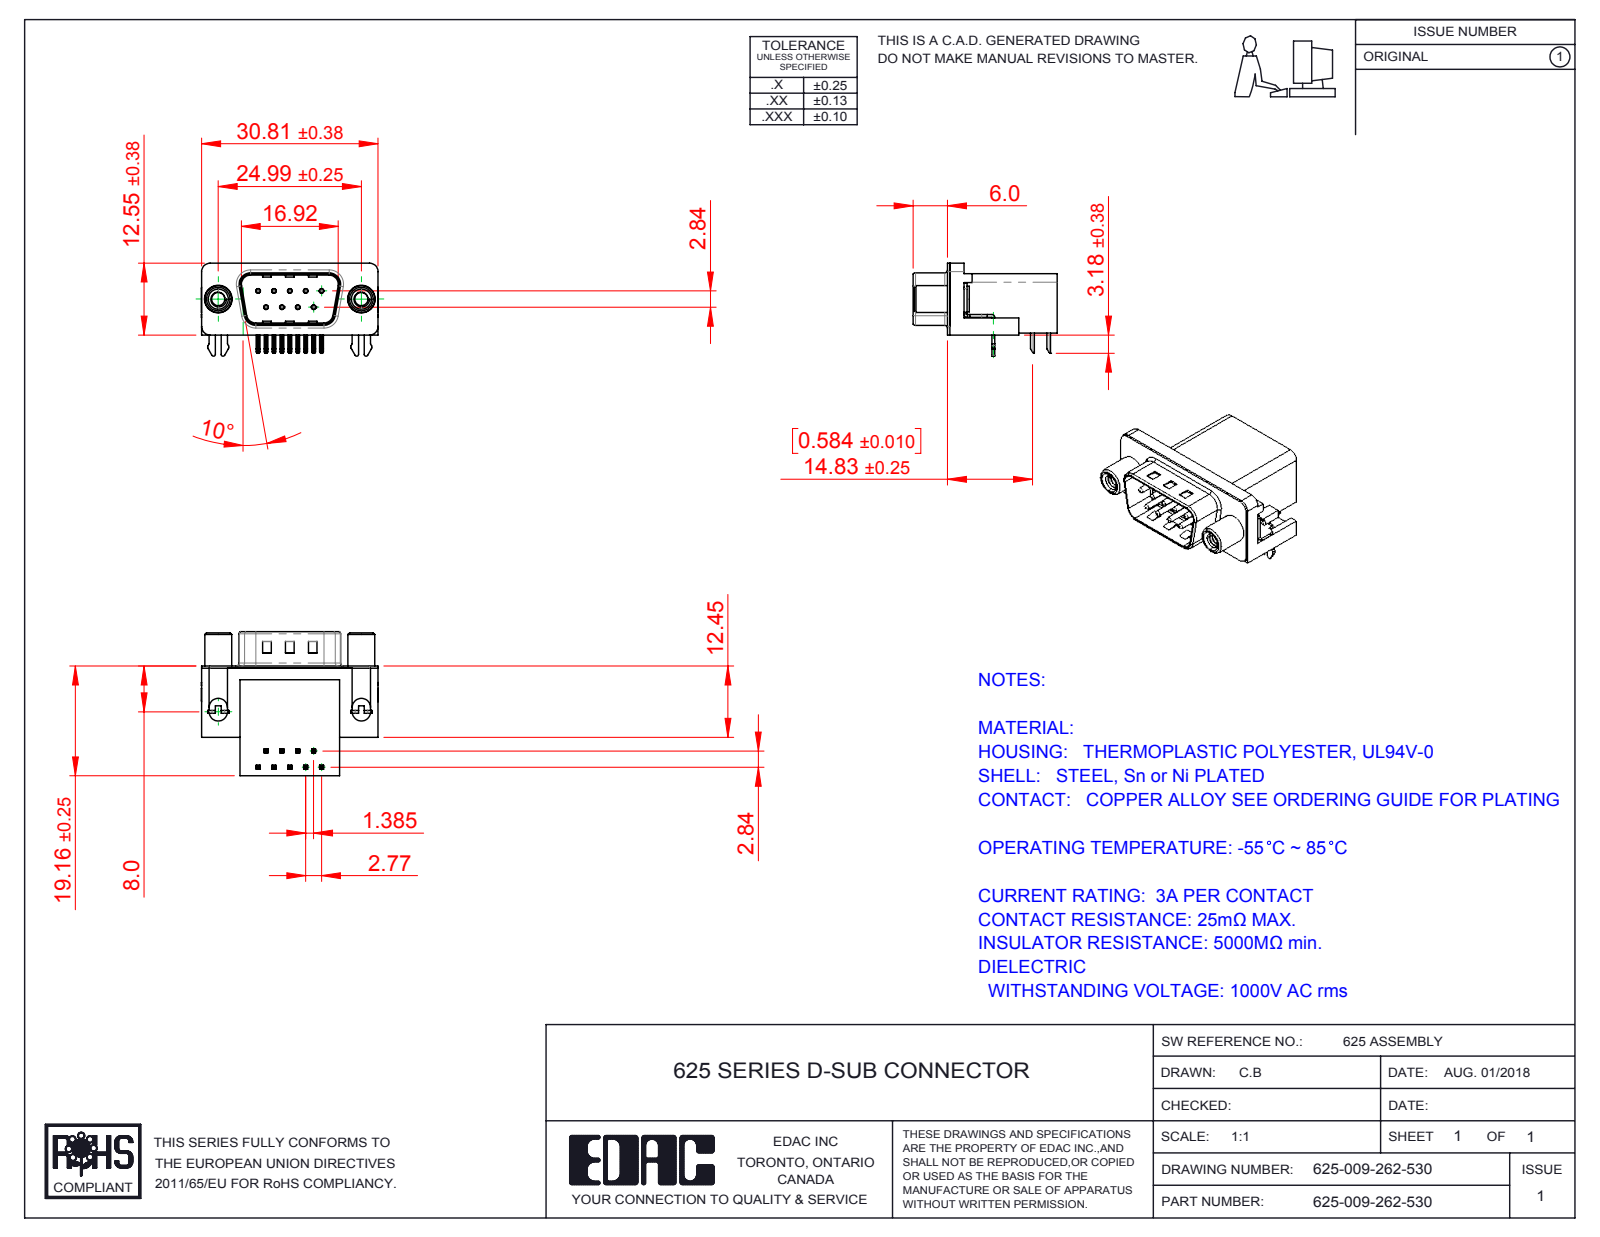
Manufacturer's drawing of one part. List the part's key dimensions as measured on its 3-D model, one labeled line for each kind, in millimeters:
Part name (STEP PRODUCT): 625 Housing_9 Socket; 625-009-262-530; 625 Contact Top; 625 Round Threaded Standoff (+3 more)
STEP written by: SolidWorks 2016 (CONFIG_CONTROL_DESIGN)
Units: millimetres
Bodies: 15 solids, 1027 faces (597 planar, 333 cylindrical, 97 other)
Overall size (bounding box): 30.89 × 25.16 × 16.25
Volume: 4 565 mm³ · Surface area: 5 156 mm²
Round holes (diameter × count): ⌀0.35 ×9, ⌀0.8 ×9, ⌀2.3 ×2, ⌀3.1 ×2, ⌀4 ×2, ⌀4.8 ×2, ⌀5 ×2
Round bosses / shafts (diameter × count): ⌀0.75 ×9, ⌀4.9 ×2, ⌀4.7 ×2, ⌀4.5 ×2, ⌀3.85 ×2
Partial cylindrical surfaces — rounded edges, fillets, slot ends (radius × count): R0.25 ×36, R0.12 ×18, R1 ×16, R0.5 ×14, R1.5 ×8, R1.6 ×8, R0.32 ×4, R0.9 ×4
Main face-to-face distances: 0.4, 10.34, 18.76, 19.16, 16.26, 2.5, 2.9, 0.35, 10.69, 6.7
Hole centre spacings: 3.16, 2.77, 5.54, 5.03, 5.04, 8.31, 7.48, 7.49
